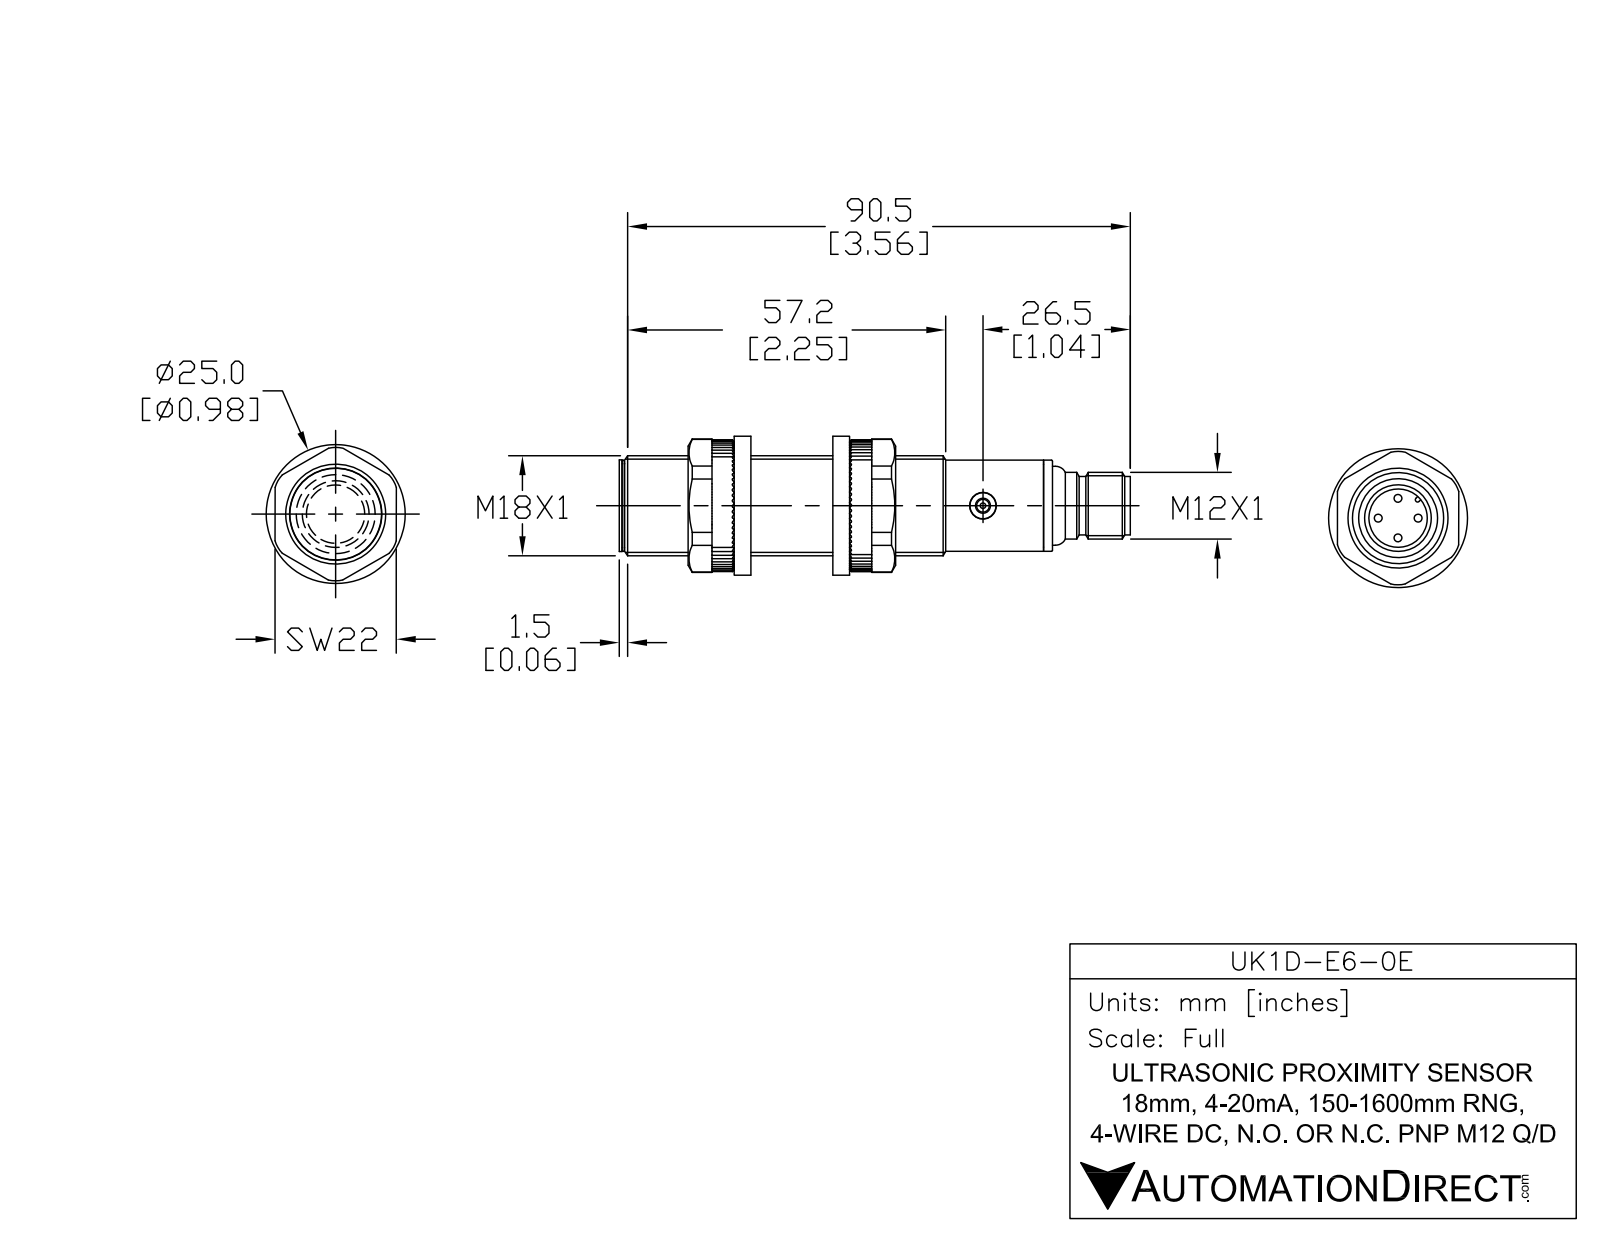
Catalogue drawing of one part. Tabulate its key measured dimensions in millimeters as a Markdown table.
| quantity | value |
| --- | --- |
| part name | UK1D-E6-0E |
| STEP written by | SolidWorks 2017 (AUTOMOTIVE_DESIGN) |
| units | millimeters |
| bodies | 6 solids, 106 faces (21 planar, 48 cylindrical, 37 other) |
| overall size | 91.6 × 18 × 18 |
| volume | 19 700 mm³ |
| surface area | 6 890 mm² |
| round holes (diameter × count) | 2.7 × 1, 4.7 × 1, 7 × 1, 8.3 × 1, 9.5 × 1 |
| round bosses / shafts (diameter × count) | 1 × 4, 18 × 1, 16.6 × 1, 16.4 × 1, 15.8 × 1, 14.2 × 1, 12 × 1, 10.5 × 1 |
| partial cylindrical surfaces (radius × count) | 0.6 × 1 |
| main face-to-face distances | 75.1, 1, 76.1, 0.9, 76, 1.1, 4, 77.6, 77.5, 76.6 |
